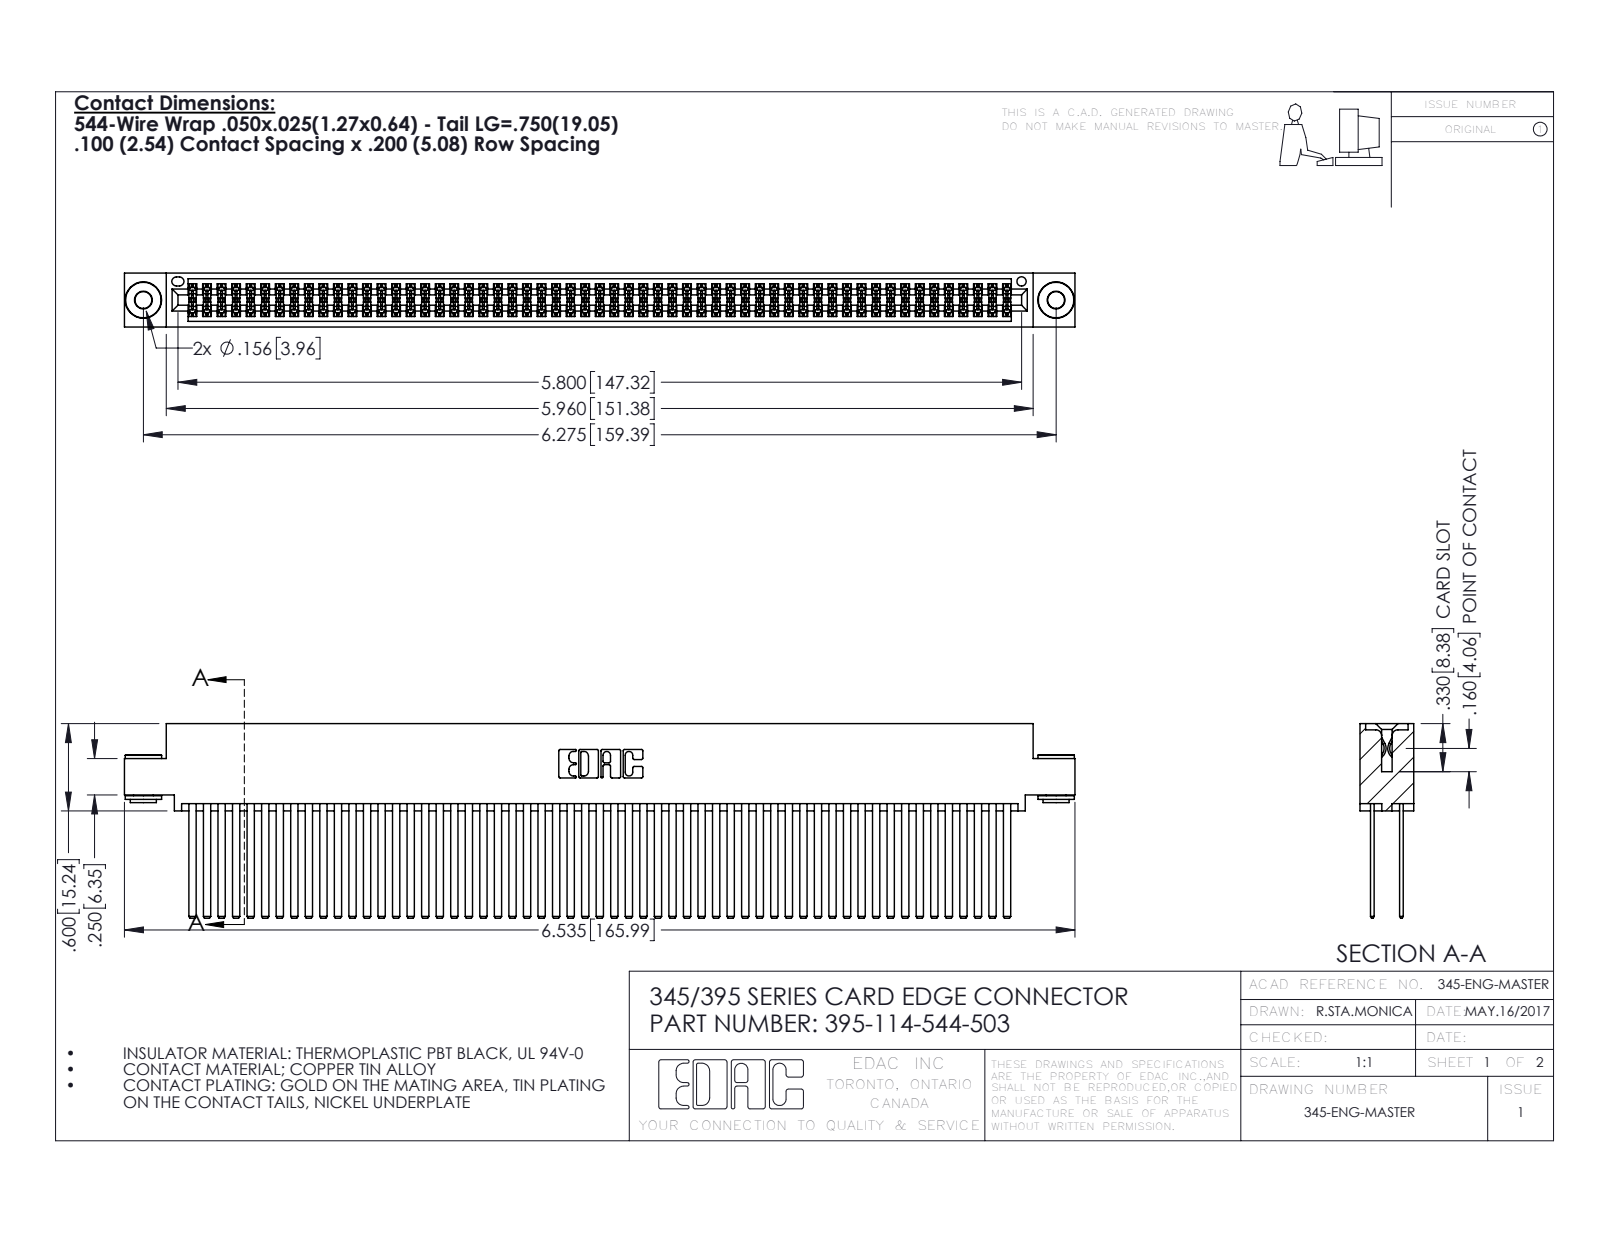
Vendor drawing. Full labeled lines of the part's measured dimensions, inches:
Part name (STEP PRODUCT): 395-114-544-503; 345 Part_0.110 Offset - 0.156 Dia-TH; 345-250-002_345-250-002-102; 345-292-001_345-293-144
STEP written by: SolidWorks 2016 (CONFIG_CONTROL_DESIGN)
Units: inches
Bodies: 117 solids, 5184 faces (3400 planar, 1776 cylindrical, 8 other)
Overall size (bounding box): 6.535 × 1.337 × 0.37
Volume: 1.087 in³ · Surface area: 48.97 in²
Round holes (diameter × count): ⌀0.116 ×2, ⌀0.156 ×2, ⌀0.064 ×1
Round bosses / shafts (diameter × count): ⌀0.25 ×2, ⌀0.18 ×2, ⌀0.136 ×2
Partial cylindrical surfaces — rounded edges, fillets, slot ends (radius × count): R0.006 ×171, R0.01 ×22, R0.007 ×6, R0.031 ×6, R0.026 ×3, R0.014 ×2, R0.019 ×2, R0.022 ×2
Main face-to-face distances: 0.2, 0.025, 0.072, 0.098, 0.272, 0.298, 0.225, 0.175, 0.37, 0.05
Hole centre spacings: 0.27, 6.039, 6.275
